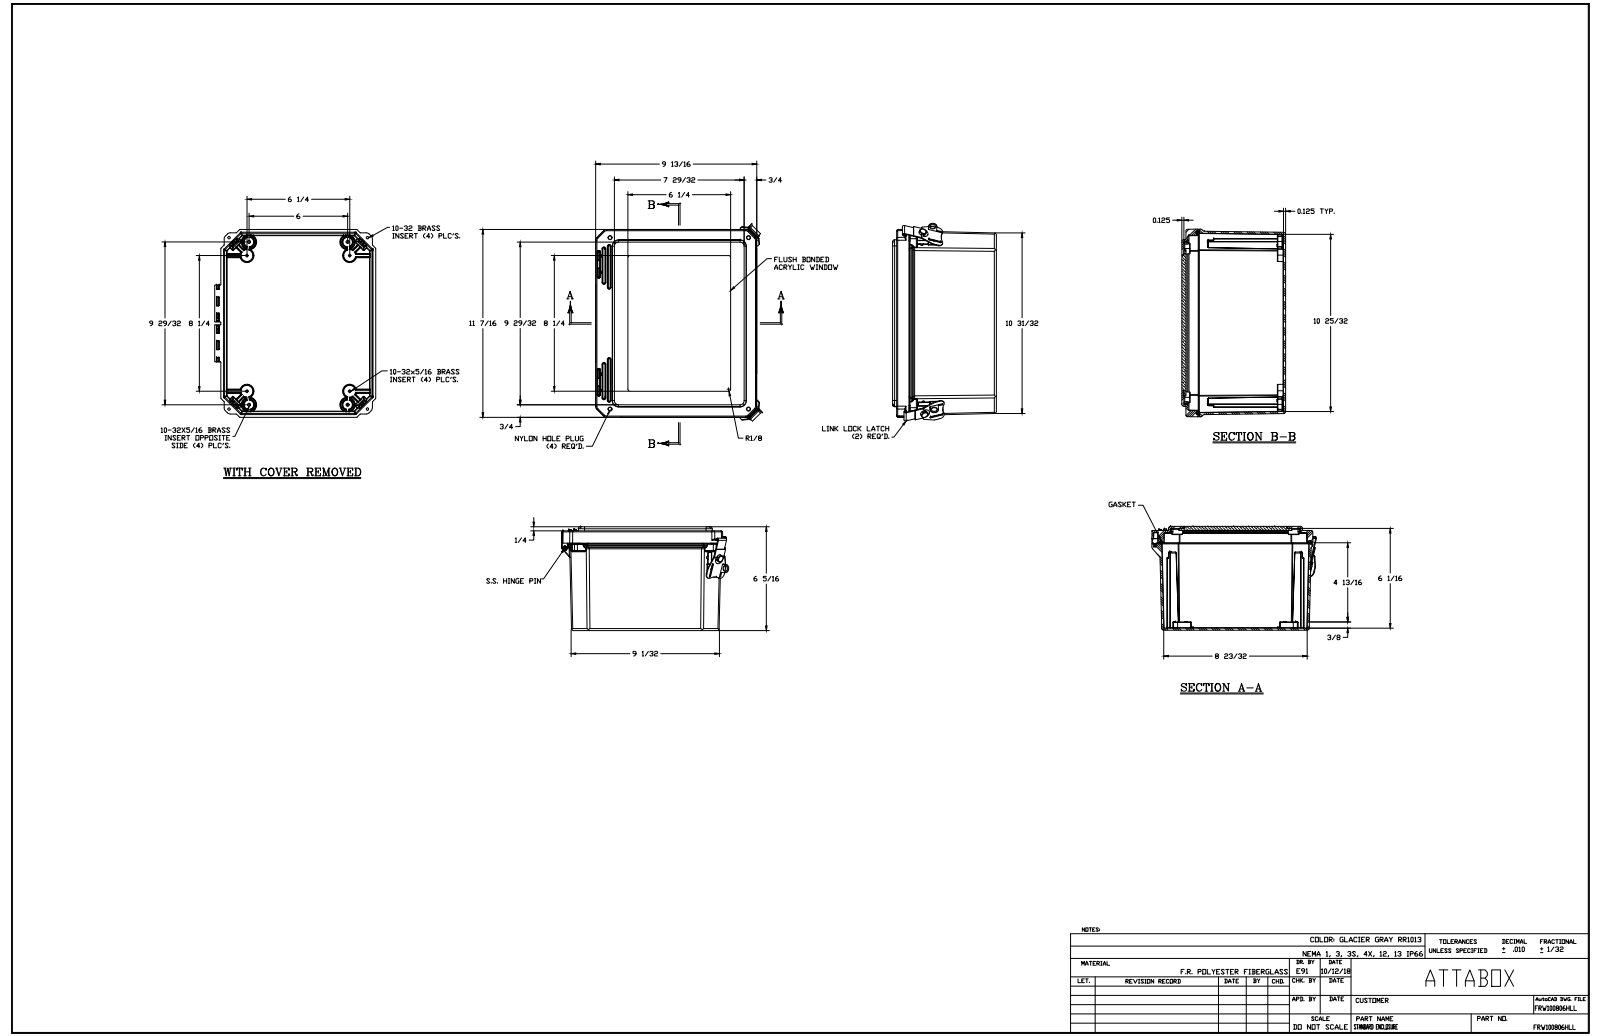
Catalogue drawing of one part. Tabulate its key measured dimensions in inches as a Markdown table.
| quantity | value |
| --- | --- |
| part name | FRW100806HLL |
| STEP written by | SolidWorks 2018 (AUTOMOTIVE_DESIGN) |
| units | inches |
| bodies | 34 solids, 2258 faces (762 planar, 896 cylindrical, 600 other) |
| overall size | 12.329 × 10.255 × 6.312 |
| volume | 76.84 in³ |
| surface area | 1 040 in² |
| round holes (diameter × count) | 0.156 × 12, 0.152 × 8, 0.098 × 4, 0.15 × 4, 0.252 × 4, 0.253 × 4, 0.05 × 2, 0.12 × 2, 0.137 × 2, 0.219 × 2, 0.227 × 2, 0.313 × 2 |
| round bosses / shafts (diameter × count) | 0.246 × 12, 0.87 × 4, 0.209 × 4, 0.2 × 4, 0.6 × 2, 0.135 × 2, 0.05 × 2, 0.435 × 1 |
| partial cylindrical surfaces (radius × count) | 0.01 × 177, 0.005 × 80, 0.02 × 57, 0.03 × 45, 0.125 × 38, 0.039 × 28, 0.03 × 24, 0.09 × 24 |
| main face-to-face distances | 0.125, 6.187, 0.127, 0.126, 6.312, 6.087, 5.963, 0.225, 0.1, 6.063 |
| hole center spacings | 9.399, 9.776, 10.229, 0.831, 1.24, 1.536, 6.18, 7.216 |
